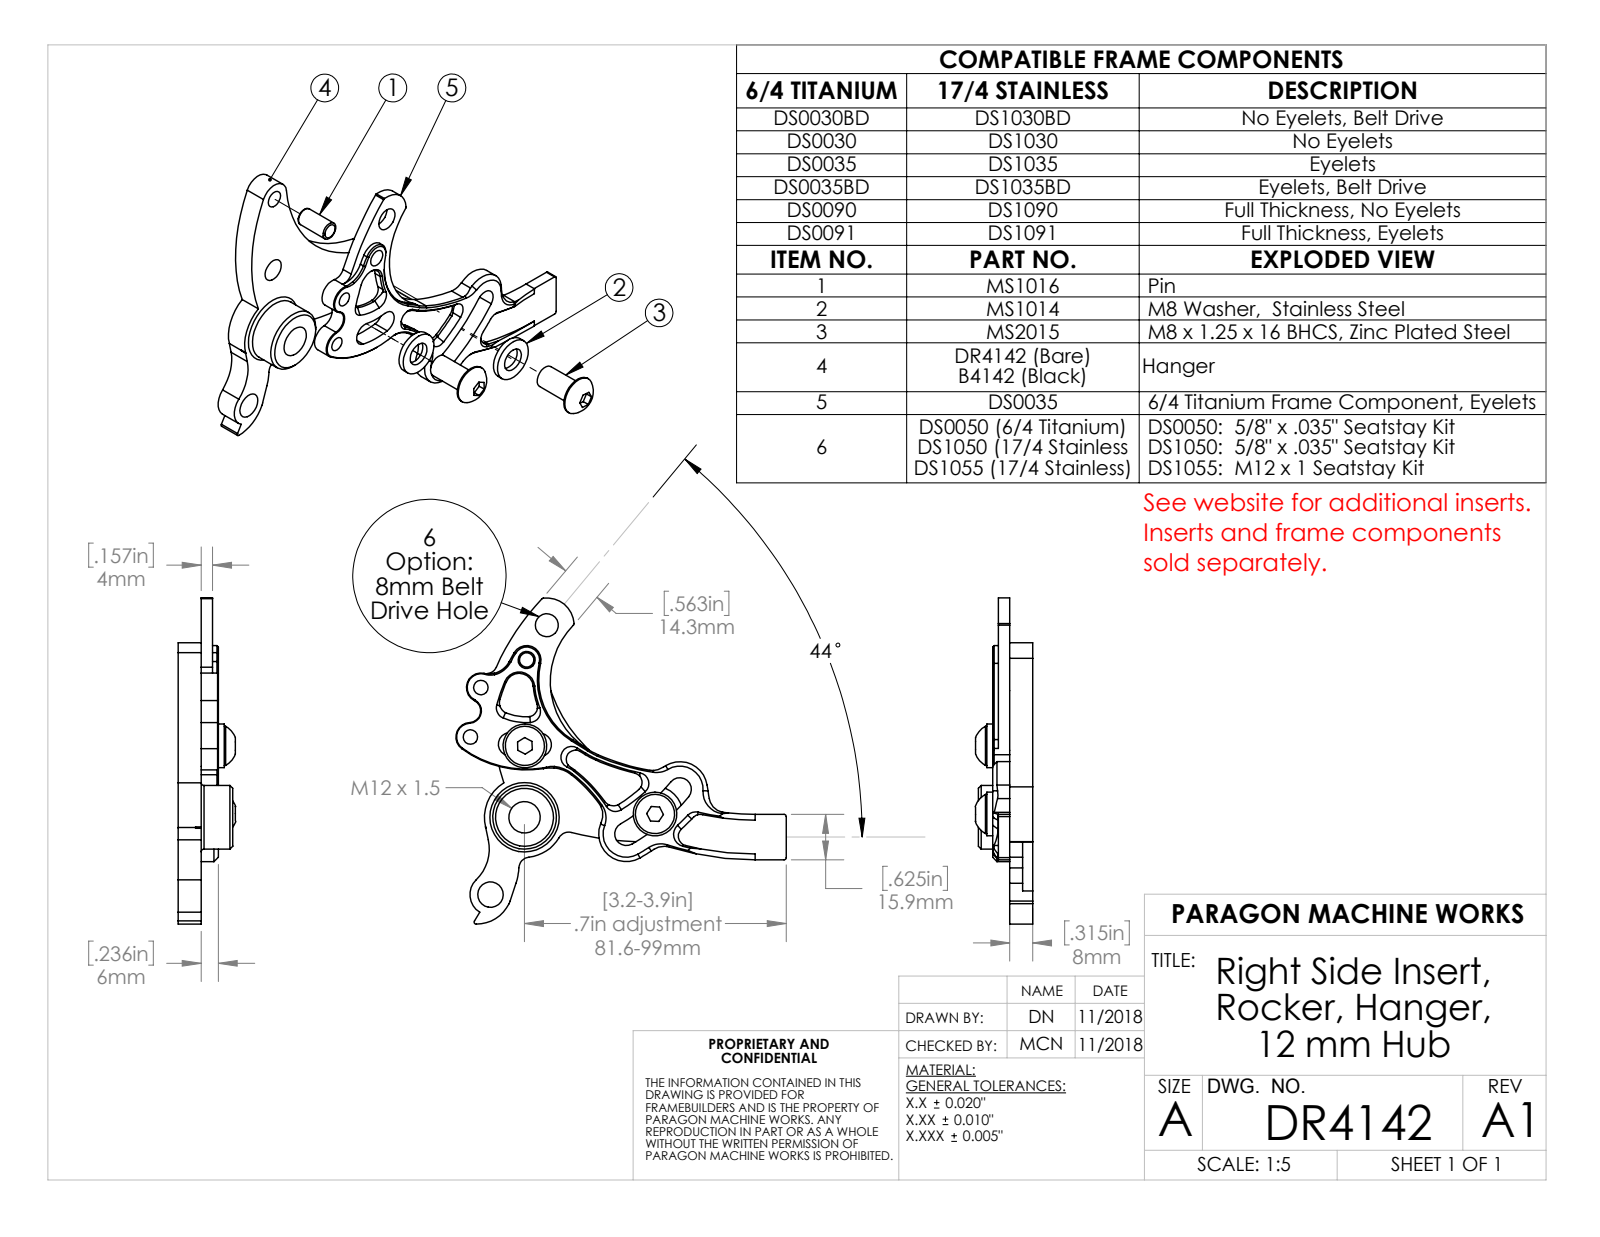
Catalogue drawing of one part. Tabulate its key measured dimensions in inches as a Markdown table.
| quantity | value |
| --- | --- |
| part name | MS1014; ROCKER_PIN; DS1035R; DR4042 (+2 more) |
| STEP written by | SolidWorks 2018 (AUTOMOTIVE_DESIGN) |
| units | inches |
| bodies | 7 solids, 260 faces (53 planar, 141 cylindrical, 66 other) |
| overall size | 4.542 × 4.483 × 0.792 |
| volume | 2.148 in³ |
| surface area | 34.11 in² |
| round holes (diameter × count) | 0.2 × 2, 0.327 × 2, 0.236 × 1, 0.315 × 1, 0.315 × 1, 0.316 × 1, 0.35 × 1, 0.433 × 1, 0.477 × 1 |
| round bosses / shafts (diameter × count) | 0.6 × 2, 0.539 × 2, 0.875 × 1, 0.315 × 1, 0.25 × 1 |
| partial cylindrical surfaces (radius × count) | 0.15 × 5, 0.16 × 5, 0.03 × 4, 0.13 × 3, 0.25 × 3, 0.38 × 3, 0.157 × 2, 0.199 × 2 |
| main face-to-face distances | 0.315, 0.551, 0.236, 0.138, 0.177, 0.374, 0.472, 0.294, 0.157, 0.079 |
| hole center spacings | 0.552, 0.695, 0.735, 0.759, 0.981, 1.004, 1.161, 1.181 |
